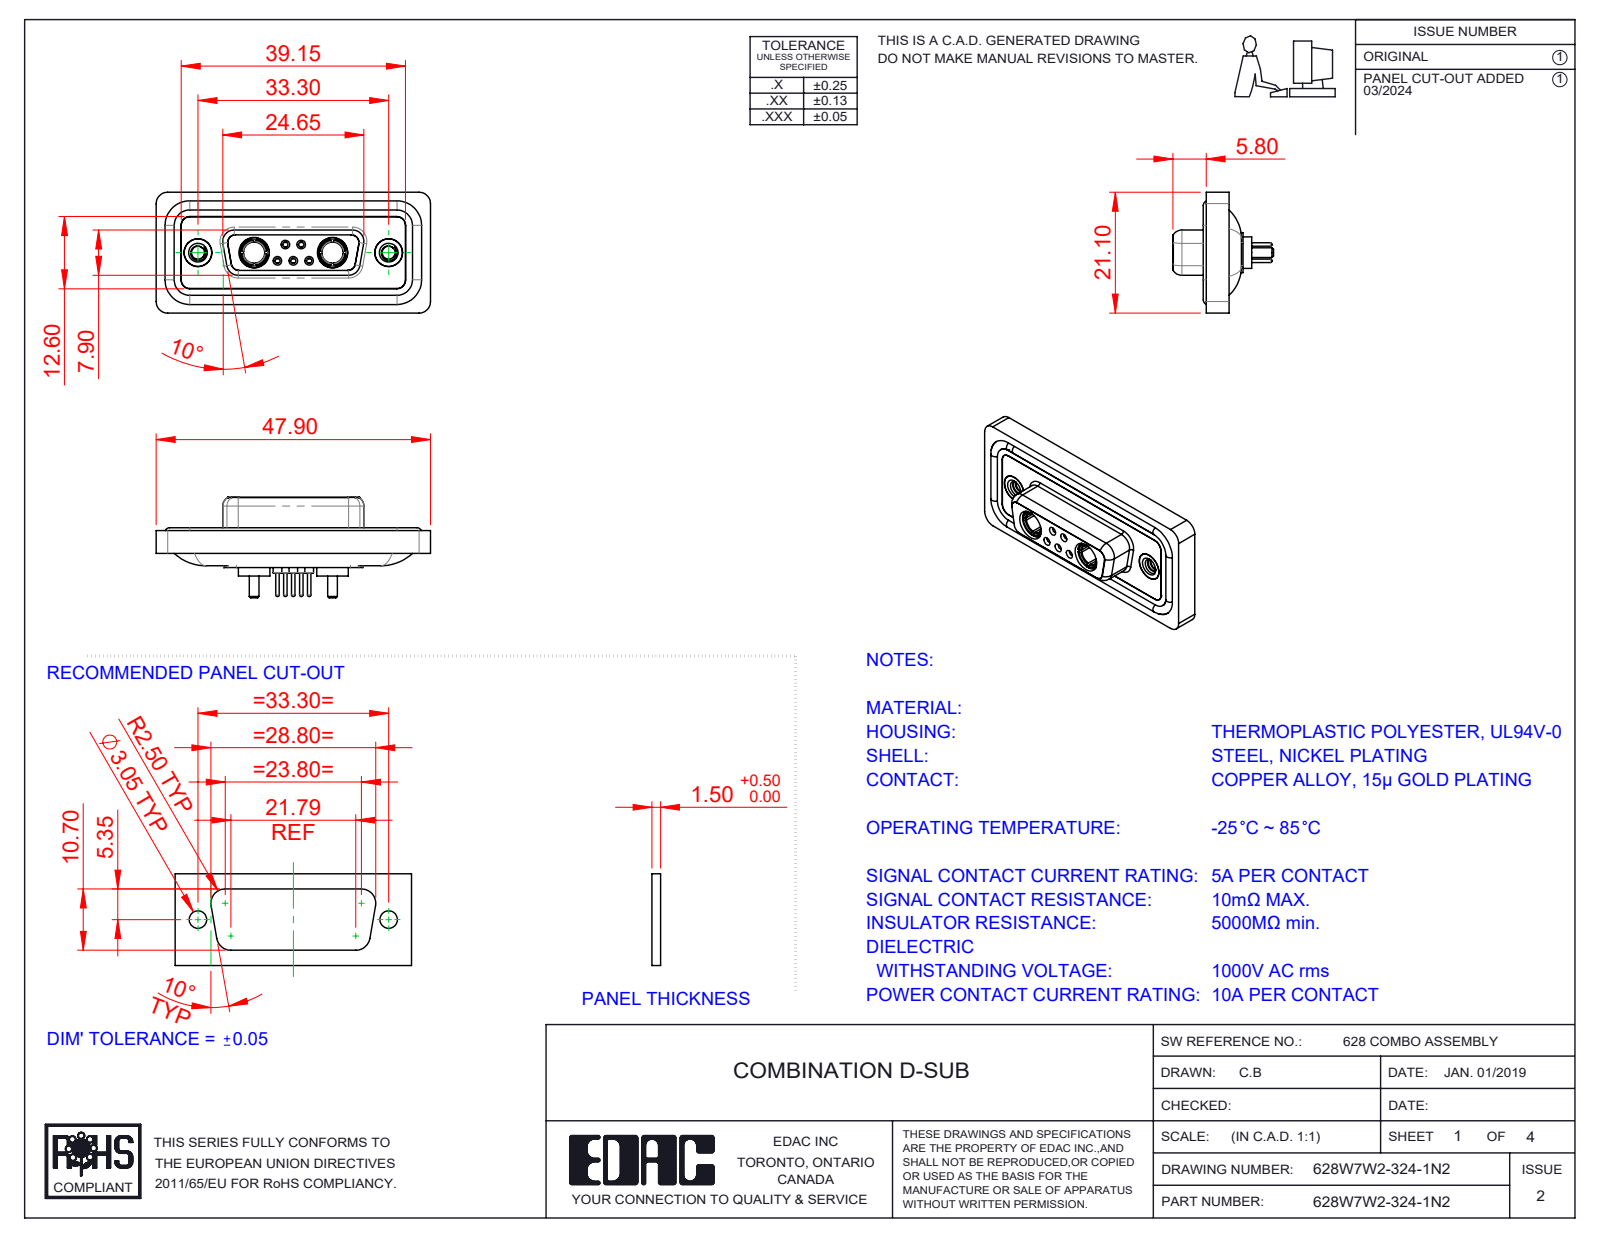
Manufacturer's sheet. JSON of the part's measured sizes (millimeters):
{"part_name": "628Combo Contact Row 2_24; Power Socket_10A S; 628Combo Contact Row 1_24; 628Combo Shell Front_15 Contacts (+5 more)", "step_written_by": "SolidWorks 2023 (CONFIG_CONTROL_DESIGN)", "units": "millimeters", "bodies": {"solids": 16, "faces": 809, "planar": 238, "cylindrical": 329, "other": 242}, "overall_size": [47.9, 21.1, 17.55], "volume_mm3": 6048, "surface_area_mm2": 9860, "round_holes": [[0.9, 5], [1.1, 5], [1.5, 5], [2, 5], [4.85, 4], [1.6, 3], [1.7, 2], [2.26, 2], [3.7, 2], [4, 2], [4.05, 2], [5, 2]], "round_bosses_or_shafts": [[1.6, 6], [2.2, 5], [0.6, 5], [5.5, 2], [5.2, 2], [4.96, 2], [4.95, 2], [4.8, 2]], "partial_cylinders_radius": [[1.5, 22], [2, 20], [1.35, 12], [1.6, 8], [0.25, 4], [0.5, 4], [0.6, 4], [0.65, 4]], "face_to_face_distances": [0.4, 1.8, 1.6, 0.5, 2.9, 1.1, 7.45, 5.65, 6.6, 7.05], "hole_center_spacings": [3.16, 2.77, 9.8, 23.5, 4.31, 4.33, 5.03, 5.04]}
